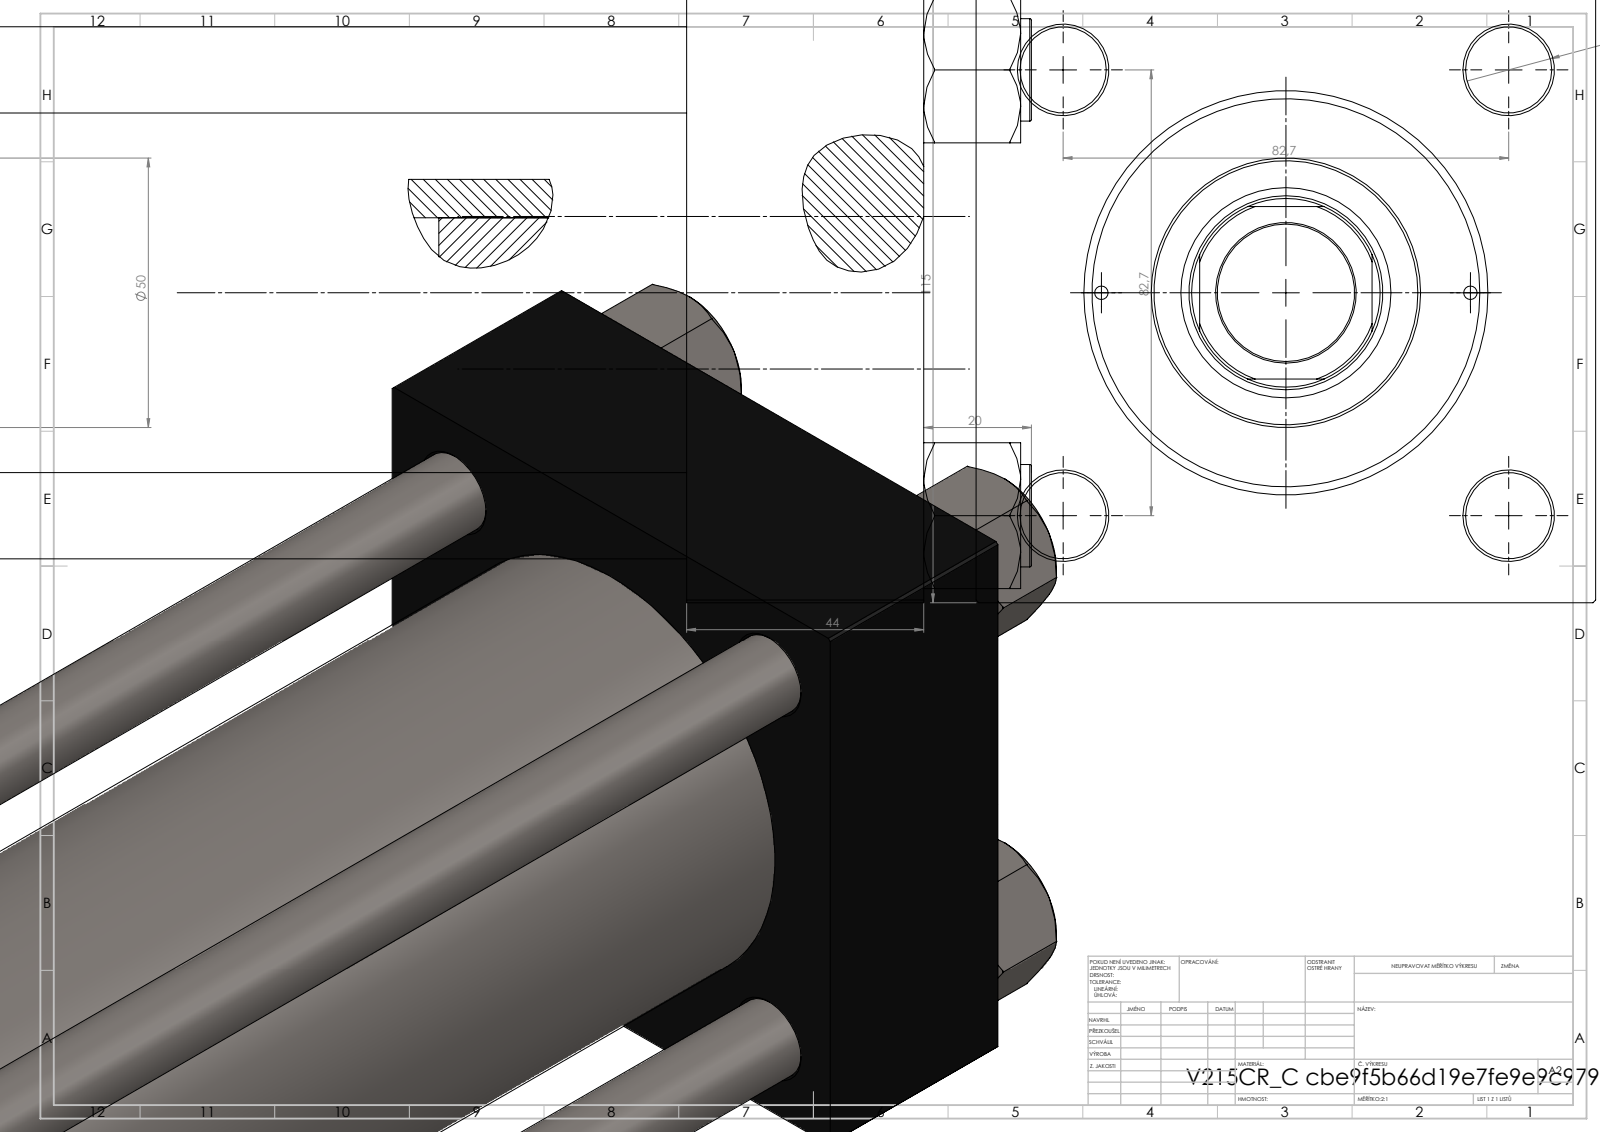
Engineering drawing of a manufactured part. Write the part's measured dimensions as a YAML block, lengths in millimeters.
part_name: "NUT_M5_C; V215CR_C_Body; V215CR_C_TYCINKA; V215_VC_A (+1 more)"
step_written_by: "SolidWorks 2019 (CONFIG_CONTROL_DESIGN)"
units: millimeters
bodies: {solids: 11, faces: 1203, planar: 576, cylindrical: 91, other: 536}
overall_size: [460, 115, 115]
volume: 2385000
surface_area: 460717
round_holes:
  - {diameter: 16, count: 4}
  - {diameter: 2.5, count: 2}
  - {diameter: 7, count: 2}
  - {diameter: 26.44, count: 2}
  - {diameter: 35, count: 2}
  - {diameter: 25.5, count: 1}
  - {diameter: 36, count: 1}
  - {diameter: 39, count: 1}
  - {diameter: 61, count: 1}
  - {diameter: 72, count: 1}
  - {diameter: 80, count: 1}
round_bosses_or_shafts:
  - {diameter: 19, count: 4}
  - {diameter: 86, count: 1}
  - {diameter: 50, count: 1}
partial_cylinders:
  - {radius: 17.5, count: 1}
face_to_face_distances: [115, 44, 409, 365, 69, 340, 296, 380.3, 336.3, 40.3]
hole_center_spacings: [41.96, 58.48, 82.7, 86.17, 34.25, 116.96, 68.5, 341]
